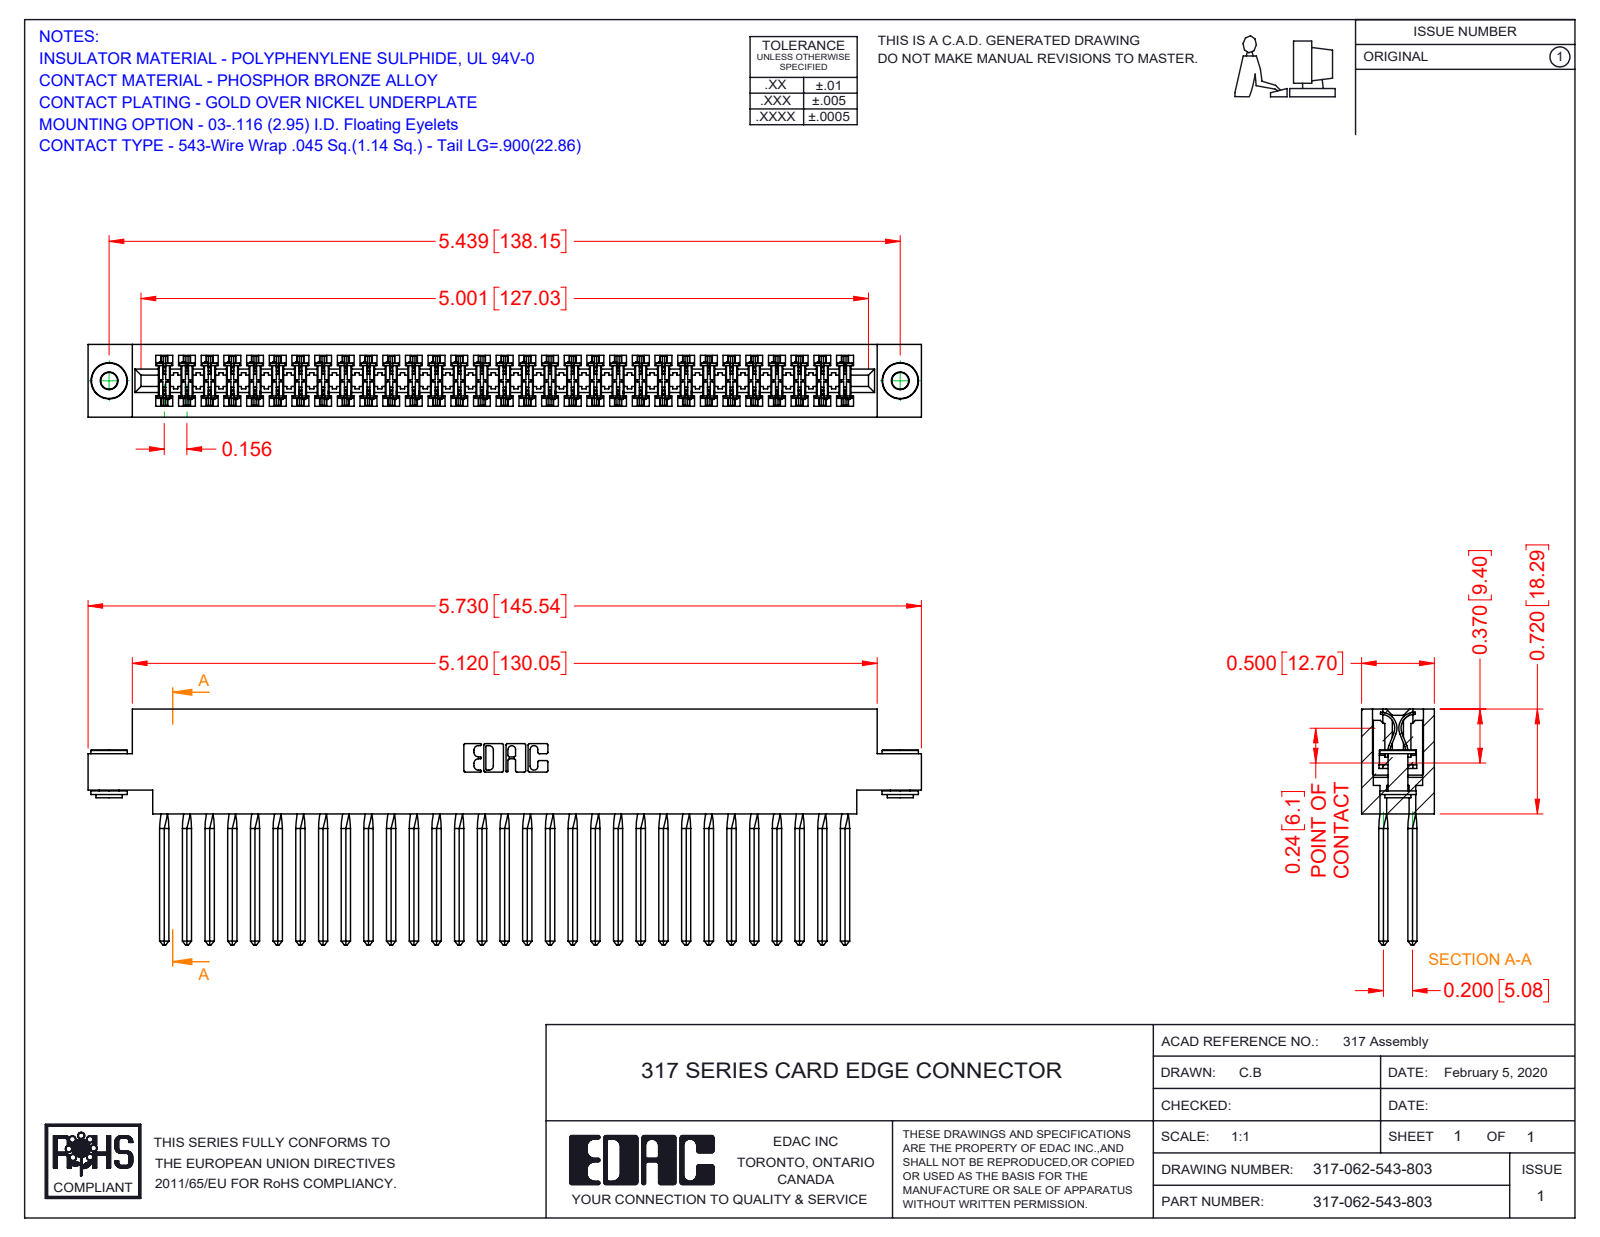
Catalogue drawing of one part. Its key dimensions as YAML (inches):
part_name: "317-062-543-803; 317-290-001_543; 345-250-002_345-250-002-102; 317 Part_.156 Dia - TH"
step_written_by: "SolidWorks 2016 (CONFIG_CONTROL_DESIGN)"
units: inches
bodies: {solids: 65, faces: 5658, planar: 4594, cylindrical: 808, other: 256}
overall_size: [5.73, 1.62, 0.5]
volume: 1.488
surface_area: 56.99
round_holes:
  - {diameter: 0.116, count: 2}
  - {diameter: 0.156, count: 2}
round_bosses_or_shafts:
  - {diameter: 0.25, count: 2}
  - {diameter: 0.18, count: 2}
  - {diameter: 0.136, count: 2}
partial_cylinders:
  - {radius: 0.015, count: 124}
  - {radius: 0.01, count: 22}
  - {radius: 0.007, count: 6}
  - {radius: 0.031, count: 6}
  - {radius: 0.026, count: 3}
  - {radius: 0.095, count: 2}
  - {radius: 0.1, count: 2}
  - {radius: 0.11, count: 2}
face_to_face_distances: [0.5, 0.075, 0.425, 0.35, 0.11, 0.195, 0.094, 0.2, 0.115, 0.131]
hole_center_spacings: [5.439]
